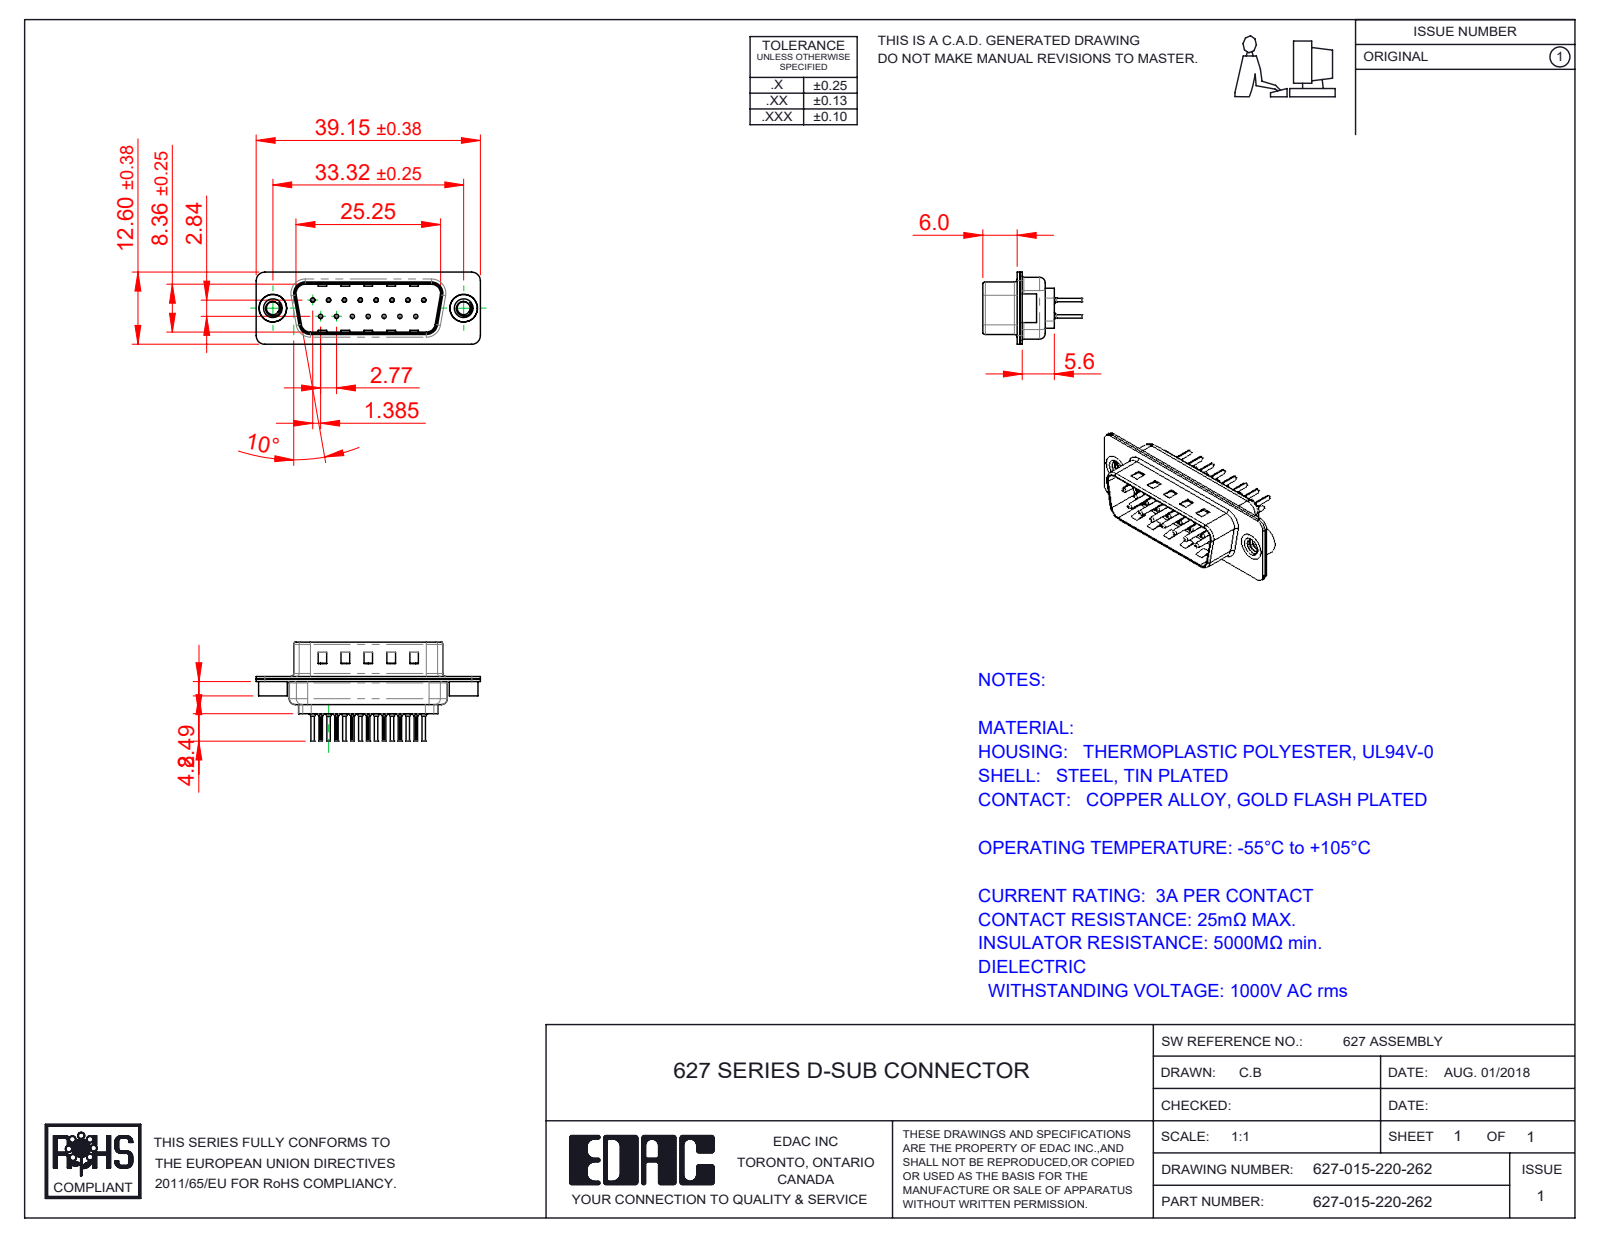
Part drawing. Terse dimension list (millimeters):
name: 627 Shell Front_15 Contacts; 627-015-220-262; 627 Housing_15 LP; 627 Contact Row 1_20L (+3 more)
written by: SolidWorks 2020 (CONFIG_CONTROL_DESIGN)
unit: mm
bodies: 20 solids, 1806 faces (499 planar, 686 cylindrical, 621 other)
size: 39.15 × 17.3 × 12.6
volume: 1 826 mm³; area: 5 382 mm²
holes: 15× ⌀0.2, 15× ⌀0.35, 15× ⌀1.1, 15× ⌀1.6, 2× ⌀2.26, 2× ⌀4, 2× ⌀4.8
bosses: 15× ⌀2, 15× ⌀1.5, 15× ⌀0.75, 15× ⌀0.6, 2× ⌀5, 2× ⌀4.9
rounds: 30× R0.1, 16× R1.5, 12× R2, 8× R0.5, 8× R1.6, 4× R0.25, 4× R0.6, 4× R0.65
face distances: 0.4, 0.45, 0.9, 0.82, 9.58, 8.76, 1.5, 1.4, 6.5, 5.6
hole spacings: 3.16, 2.77, 5.54, 8.31, 11.08, 5.03, 5.04, 7.48
